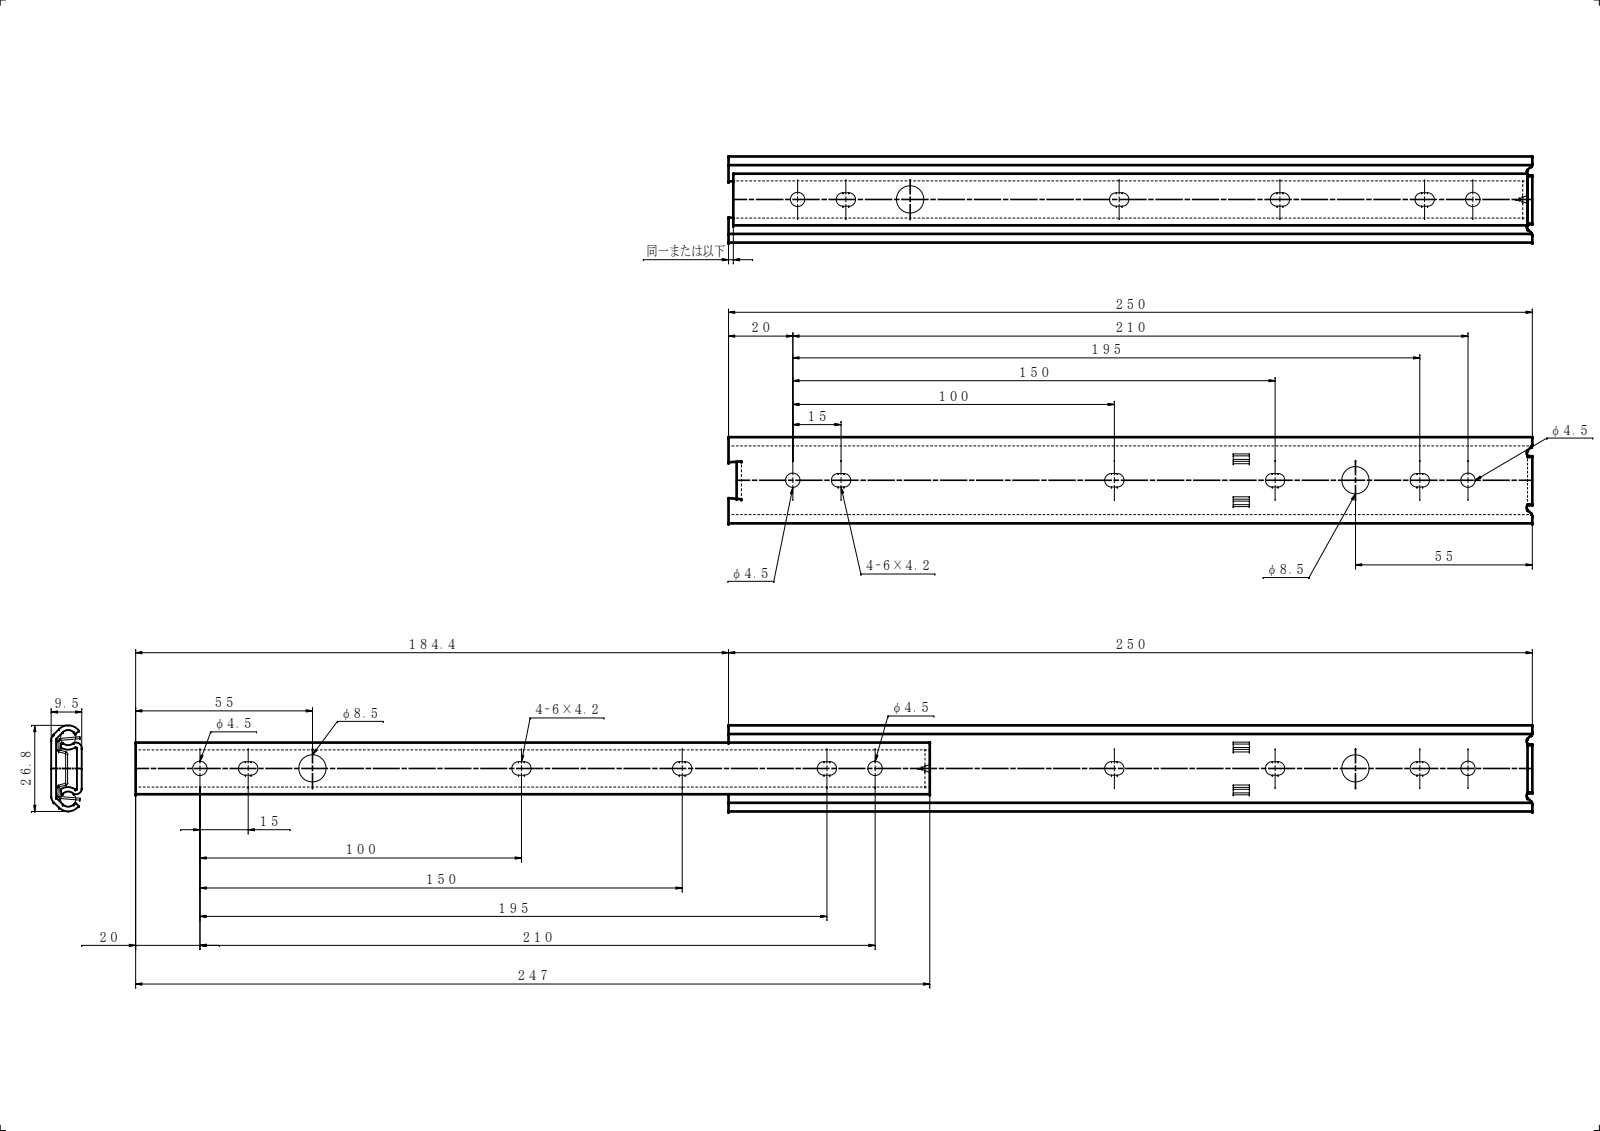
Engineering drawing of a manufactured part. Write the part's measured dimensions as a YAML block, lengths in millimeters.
part_name: "U2721_250; U2721-250 OM; U2721-250 IM"
step_written_by: "SolidWorks 2019 (CONFIG_CONTROL_DESIGN)"
units: millimeters
bodies: {solids: 2, faces: 134, planar: 61, cylindrical: 73, other: 0}
overall_size: [434.4, 26.8, 9.5]
volume: 22808
surface_area: 32662
round_holes:
  - {diameter: 4.5, count: 4}
  - {diameter: 8.5, count: 2}
partial_cylinders:
  - {radius: 2.1, count: 16}
  - {radius: 2, count: 10}
  - {radius: 1, count: 5}
  - {radius: 0.5, count: 4}
  - {radius: 0.18, count: 2}
  - {radius: 1.3, count: 2}
  - {radius: 1.68, count: 2}
  - {radius: 2.38, count: 2}
face_to_face_distances: [1.5, 8, 9.5, 6.5, 187.4, 185.9, 246.02, 58.62, 188.9, 247.52]
hole_center_spacings: [35, 149.4, 175, 184.4, 210, 359.4, 25.6, 324.4]
